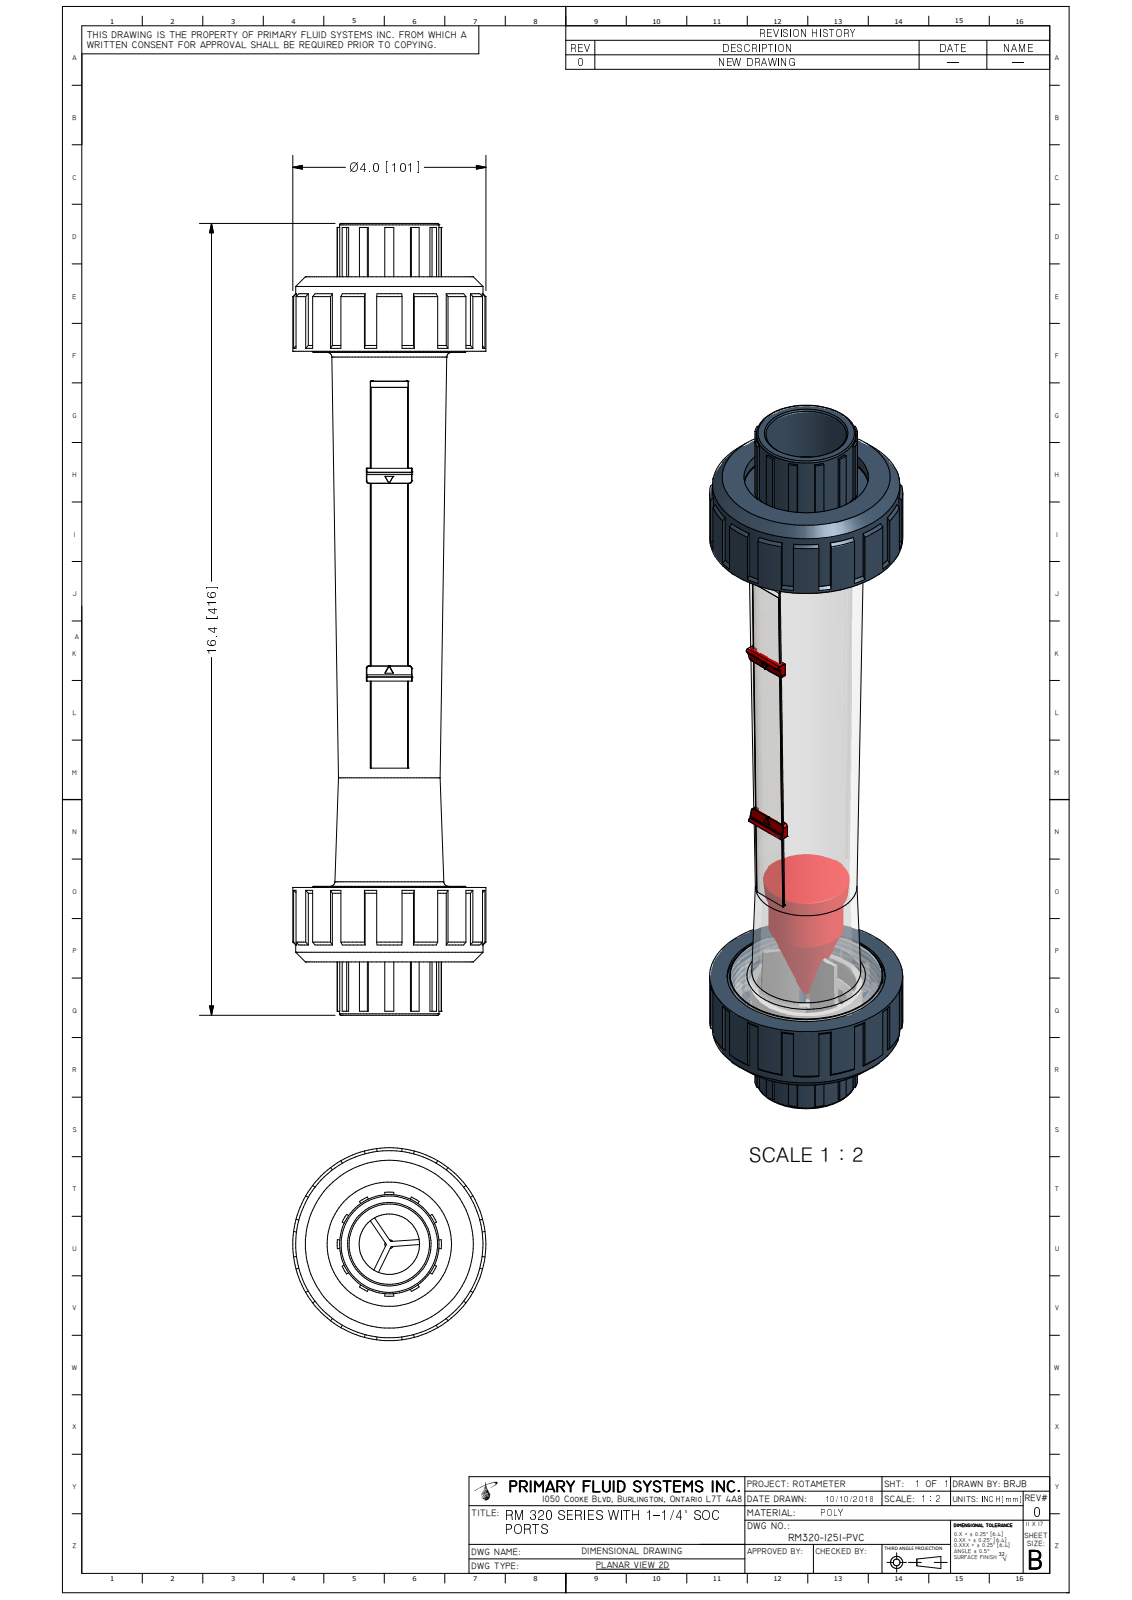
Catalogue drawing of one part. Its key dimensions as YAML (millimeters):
part_name: "RM320-125I-PVC_R0"
step_written_by: "Autodesk Inventor 2009 (AUTOMOTIVE_DESIGN)"
units: millimeters
bodies: {solids: 1, faces: 649, planar: 261, cylindrical: 128, other: 260}
overall_size: [416, 101.3, 101.3]
volume: 1298000
surface_area: 178500
round_holes:
  - {diameter: 42.2, count: 1}
  - {diameter: 65.3, count: 1}
  - {diameter: 79.9, count: 1}
  - {diameter: 82.9, count: 1}
  - {diameter: 82.9, count: 1}
round_bosses_or_shafts:
  - {diameter: 101.3, count: 1}
  - {diameter: 98.3, count: 1}
  - {diameter: 80.2, count: 1}
  - {diameter: 75.8, count: 1}
  - {diameter: 52.2, count: 1}
partial_cylinders:
  - {radius: 0.2, count: 18}
  - {radius: 0.3, count: 16}
  - {radius: 0.1, count: 8}
  - {radius: 0.2, count: 8}
  - {radius: 1.5, count: 4}
  - {radius: 0.2, count: 2}
  - {radius: 1, count: 2}
  - {radius: 27.4, count: 1}
face_to_face_distances: [39.1, 320.6, 39.6, 320.1, 0.5, 280.9, 7.6, 352.1, 31.5, 32]
